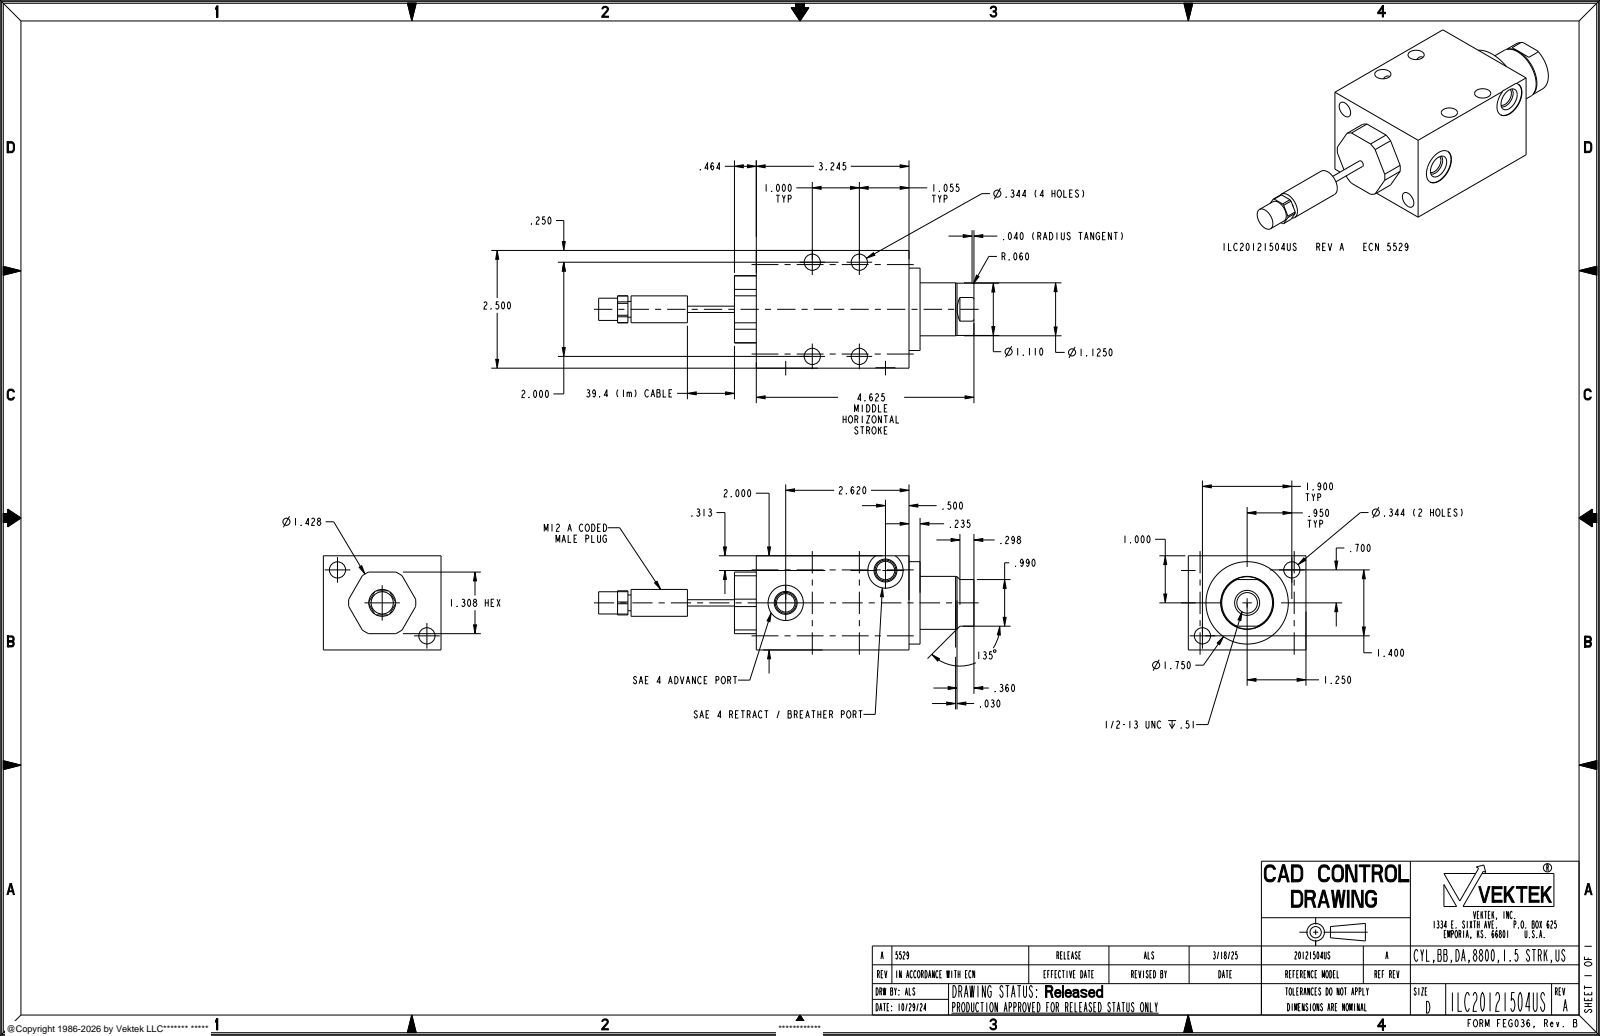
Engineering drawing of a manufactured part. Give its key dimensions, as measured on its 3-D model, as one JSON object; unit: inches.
{"part_name": "ILC20121504US", "step_written_by": "CREO PARAMETRIC BY PTC INC, 2021164 (AUTOMOTIVE_DESIGN)", "units": "inches", "bodies": {"solids": 1, "faces": 107, "planar": 36, "cylindrical": 57, "other": 14}, "overall_size": [7.975, 2.75, 2], "volume_in3": 17.52, "surface_area_in2": 66.69, "round_holes": [[0.344, 6], [0.392, 2], [0.75, 2], [0.437, 1]], "round_bosses_or_shafts": [[1.75, 1], [1.125, 1], [1.11, 1], [0.571, 1], [0.5, 1], [0.472, 1], [0.335, 1], [0.134, 1]], "partial_cylinders_radius": [[0.714, 1]], "face_to_face_distances": [2, 2.5, 3.245, 3.709, 0.464, 0.235, 3.48, 3.944, 1.308, 1.145], "hole_center_spacings": [1, 1.18, 2, 2.236, 2.229, 2.36]}
